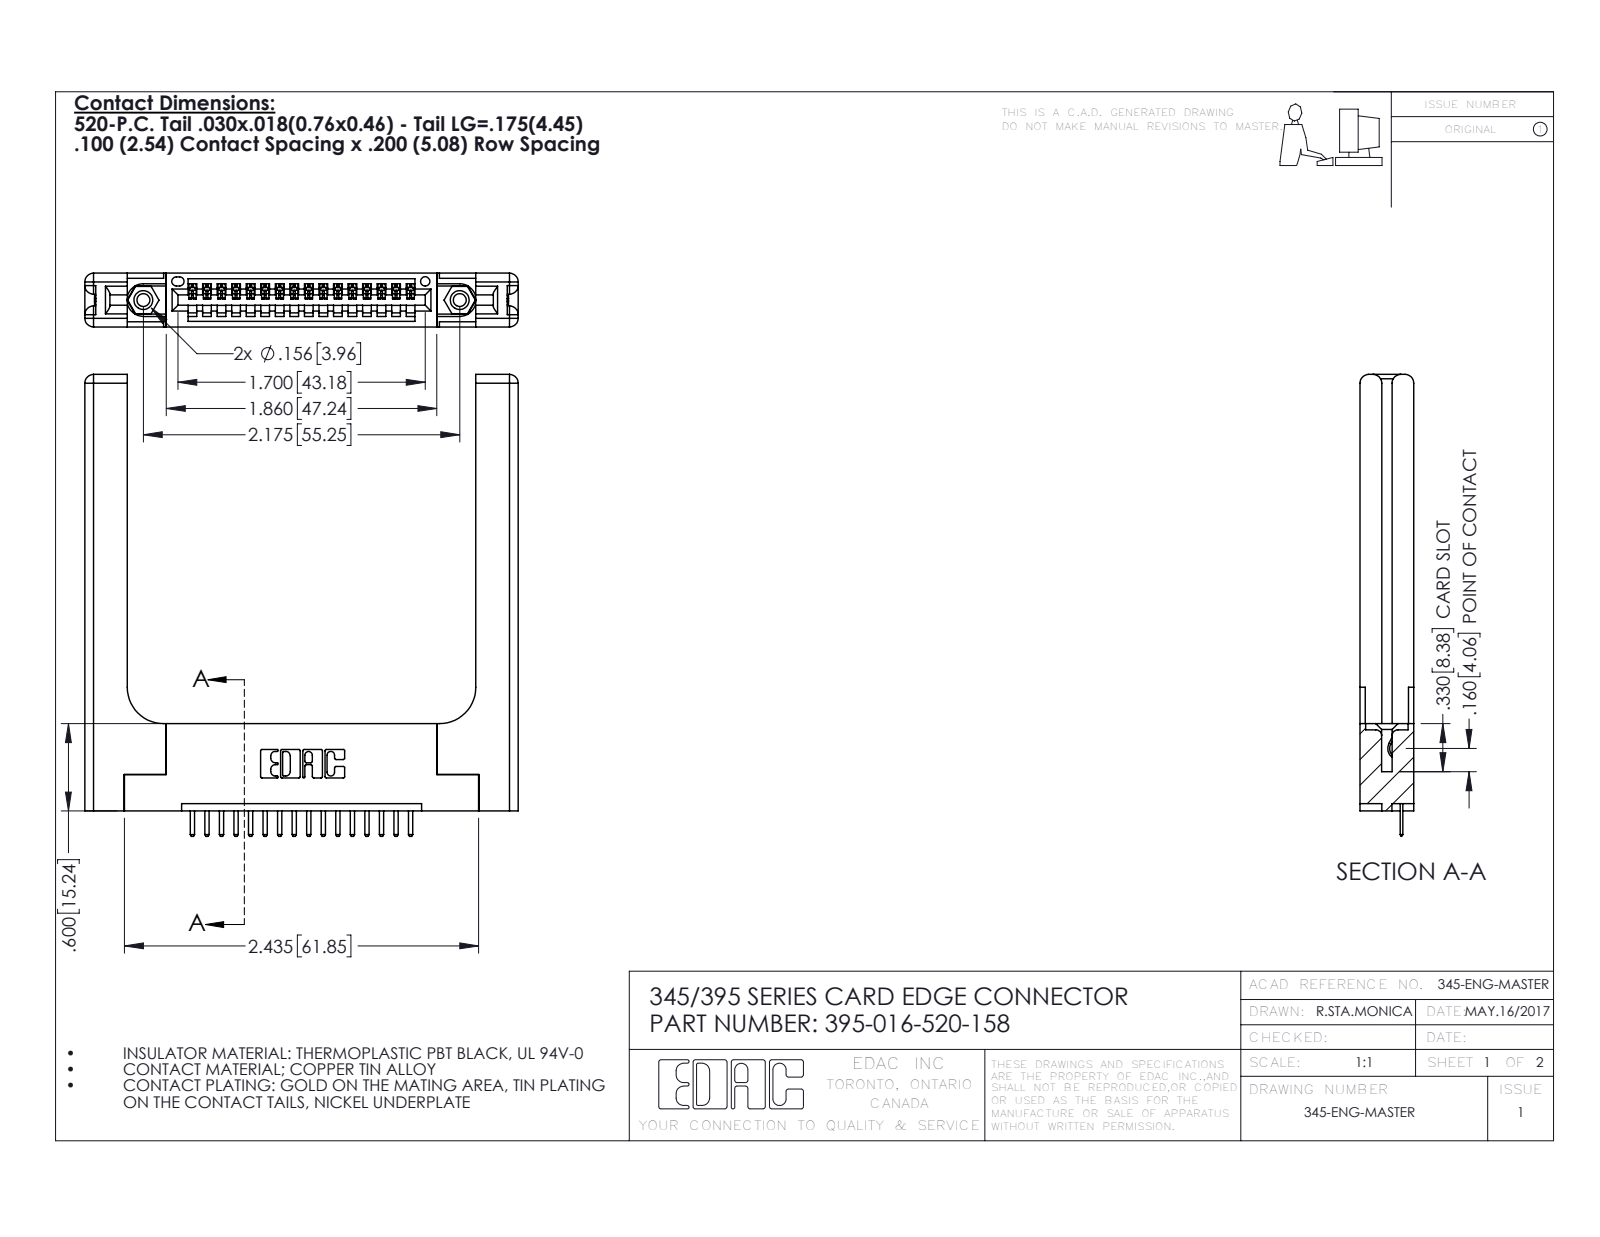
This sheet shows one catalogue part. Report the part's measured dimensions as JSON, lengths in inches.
{"part_name": "345-250-001_345-250-001-102; 395-016-520-158; 345-220-058_345-220-058; 345 Part_Flush Mounting Lugs - 0.156 Dia-TH (+1 more)", "step_written_by": "SolidWorks 2016 (CONFIG_CONTROL_DESIGN)", "units": "inches", "bodies": {"solids": 21, "faces": 1374, "planar": 900, "cylindrical": 414, "other": 60}, "overall_size": [3.175, 2.979, 0.37], "volume_in3": 0.942, "surface_area_in2": 21.71, "round_holes": [[0.089, 2], [0.125, 2], [0.156, 2], [0.064, 1]], "round_bosses_or_shafts": [[0.155, 2]], "partial_cylinders_radius": [[0.01, 34], [0.006, 32], [0.01, 22], [0.06, 16], [0.007, 6], [0.031, 6], [0.026, 3], [0.03, 2]], "face_to_face_distances": [0.37, 0.072, 0.298, 0.15, 0.077, 0.148, 0.22, 0.2, 0.225, 2.396], "hole_center_spacings": [0.27, 1.942, 2.175]}
